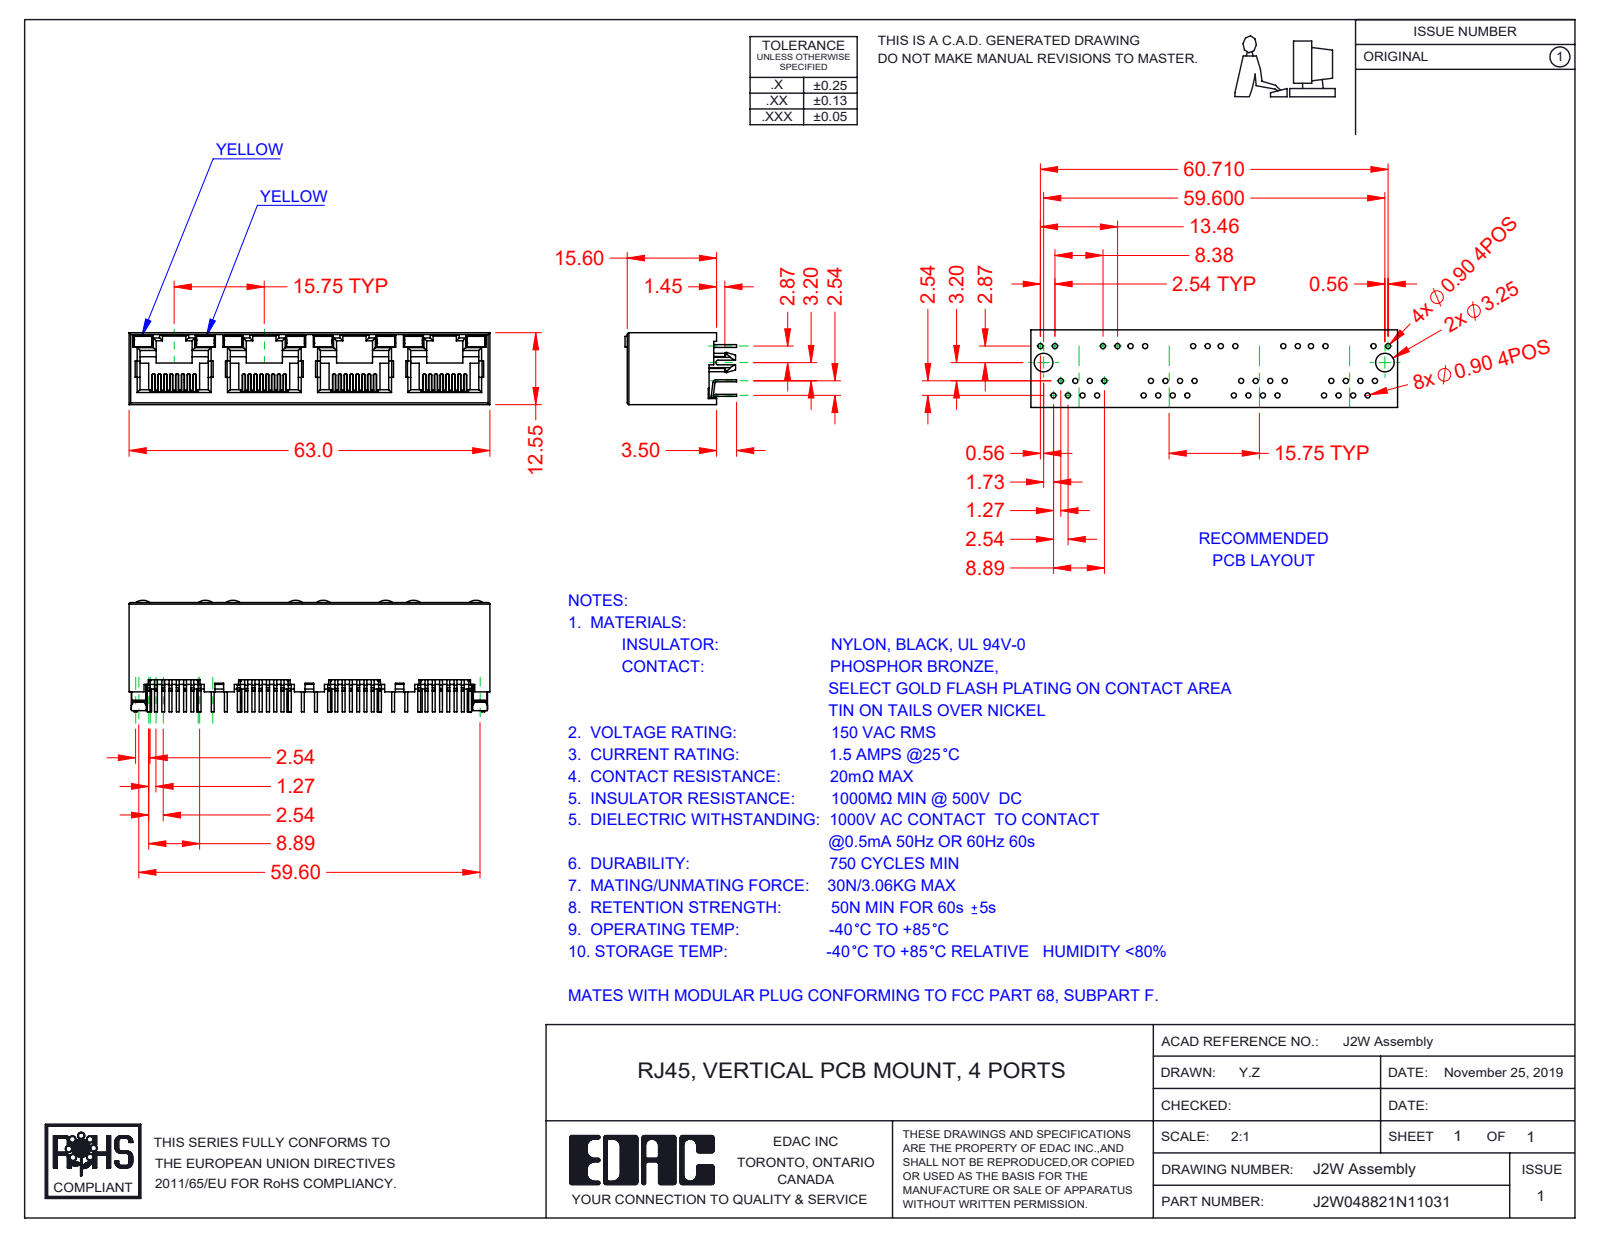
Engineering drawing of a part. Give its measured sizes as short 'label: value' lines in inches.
name: 2W Insulator; 2W Contacts; 2W LED LH_1-Yellow; 2W LED RH_1-Yellow (+2 more)
written by: SolidWorks 2016 (CONFIG_CONTROL_DESIGN)
unit: in
bodies: 45 solids, 3135 faces (2600 planar, 477 cylindrical, 58 other)
size: 2.48 × 0.768 × 0.494
volume: 0.326 in³; area: 20.37 in²
rounds: 64× R0.006, 29× R0.008, 28× R0.02, 14× R0.012, 8× R0.018, 8× R0.079, 2× R0.01, 2× R0.059
face distances: 0.494, 0.469, 0.026, 0.62, 0.014, 0.059, 0.031, 0.024, 0.445, 1.24
